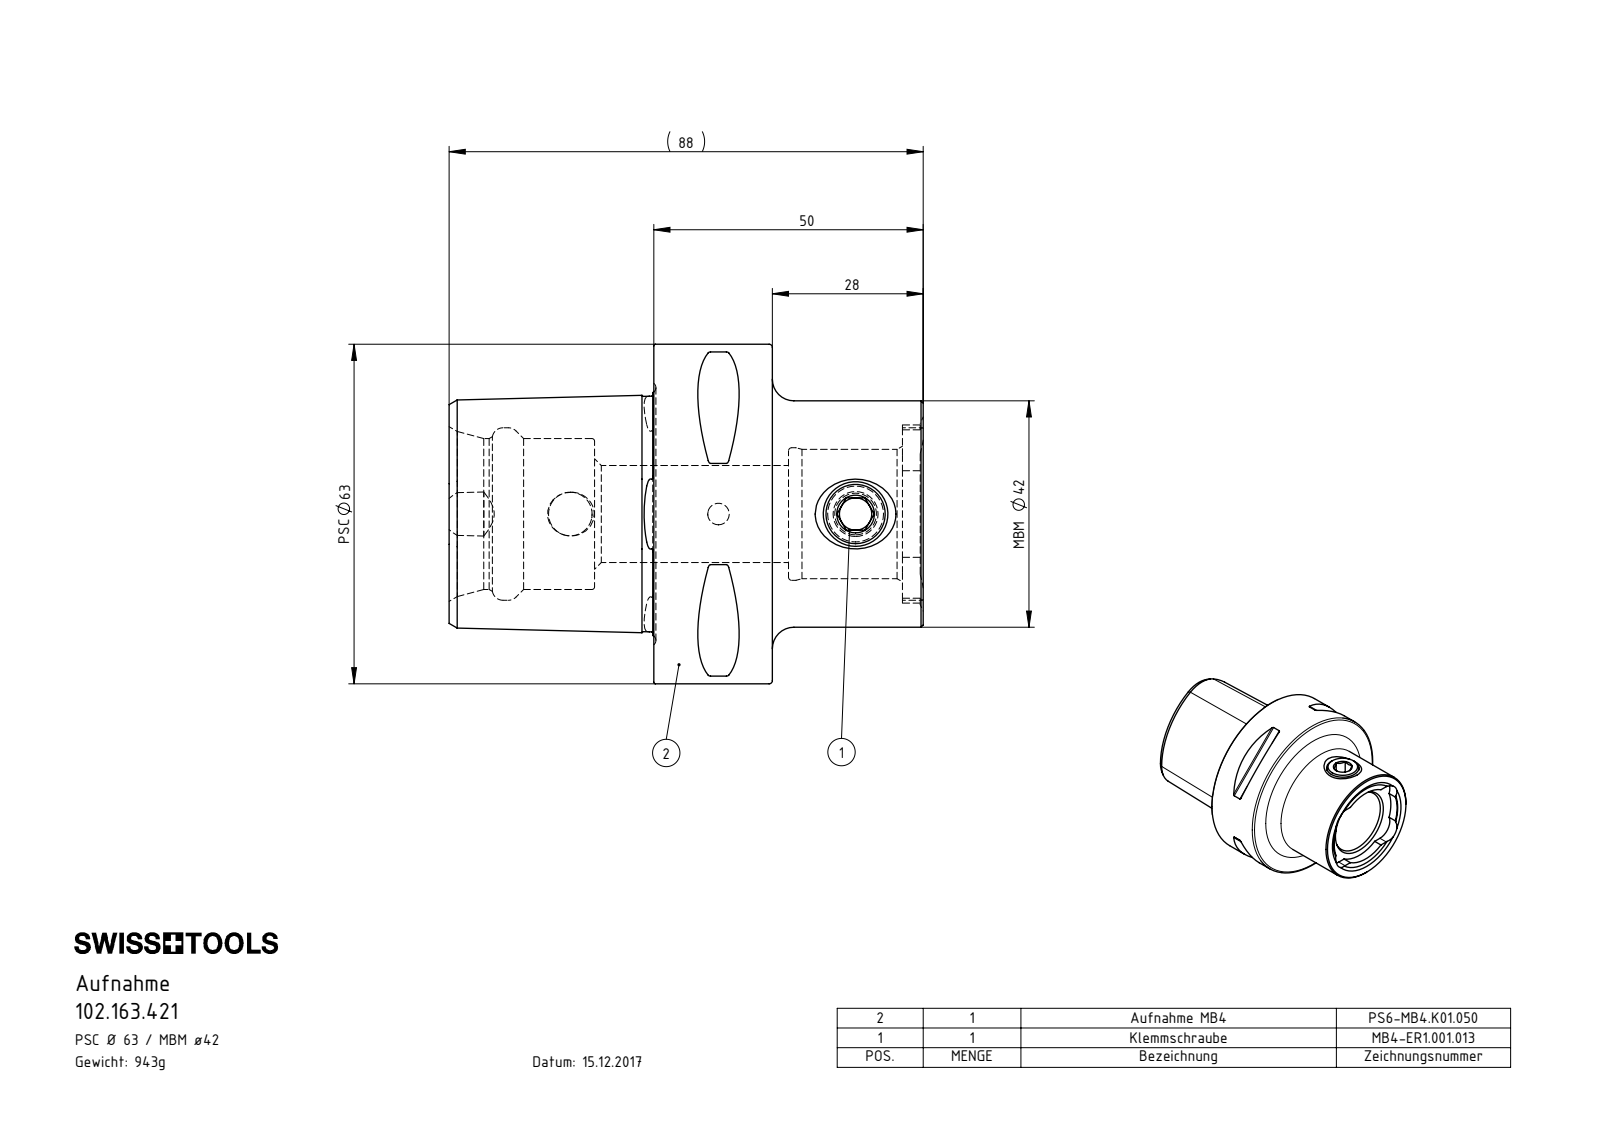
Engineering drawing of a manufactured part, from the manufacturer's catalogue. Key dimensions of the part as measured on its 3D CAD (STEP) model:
Part name (STEP PRODUCT): MB4-ER1.001.013_A; 102.163.421; PS6-MB4.K01.050_B
STEP written by: SolidWorks 2022 (CONFIG_CONTROL_DESIGN)
Units: millimetres
Bodies: 2 solids, 194 faces (44 planar, 48 cylindrical, 102 other)
Overall size (bounding box): 88 × 63 × 63
Volume: 120 144 mm³ · Surface area: 26 166 mm²
Round holes (diameter × count): ⌀4 ×1, ⌀6 ×1, ⌀8.1 ×1, ⌀11 ×1, ⌀18 ×1, ⌀24 ×1, ⌀24.6 ×1, ⌀28 ×1, ⌀32 ×1
Round bosses / shafts (diameter × count): ⌀63 ×1, ⌀42 ×1, ⌀12 ×1
Partial cylindrical surfaces — rounded edges, fillets, slot ends (radius × count): R0.5 ×8, R5.2 ×4, R6 ×1, R14.9 ×1, R16.52 ×1
Main face-to-face distances: 22, 38, 60, 25, 84.15, 46.15, 24.15, 88, 50, 28
Hole centre spacings: 25.45, 27.5, 52.95
